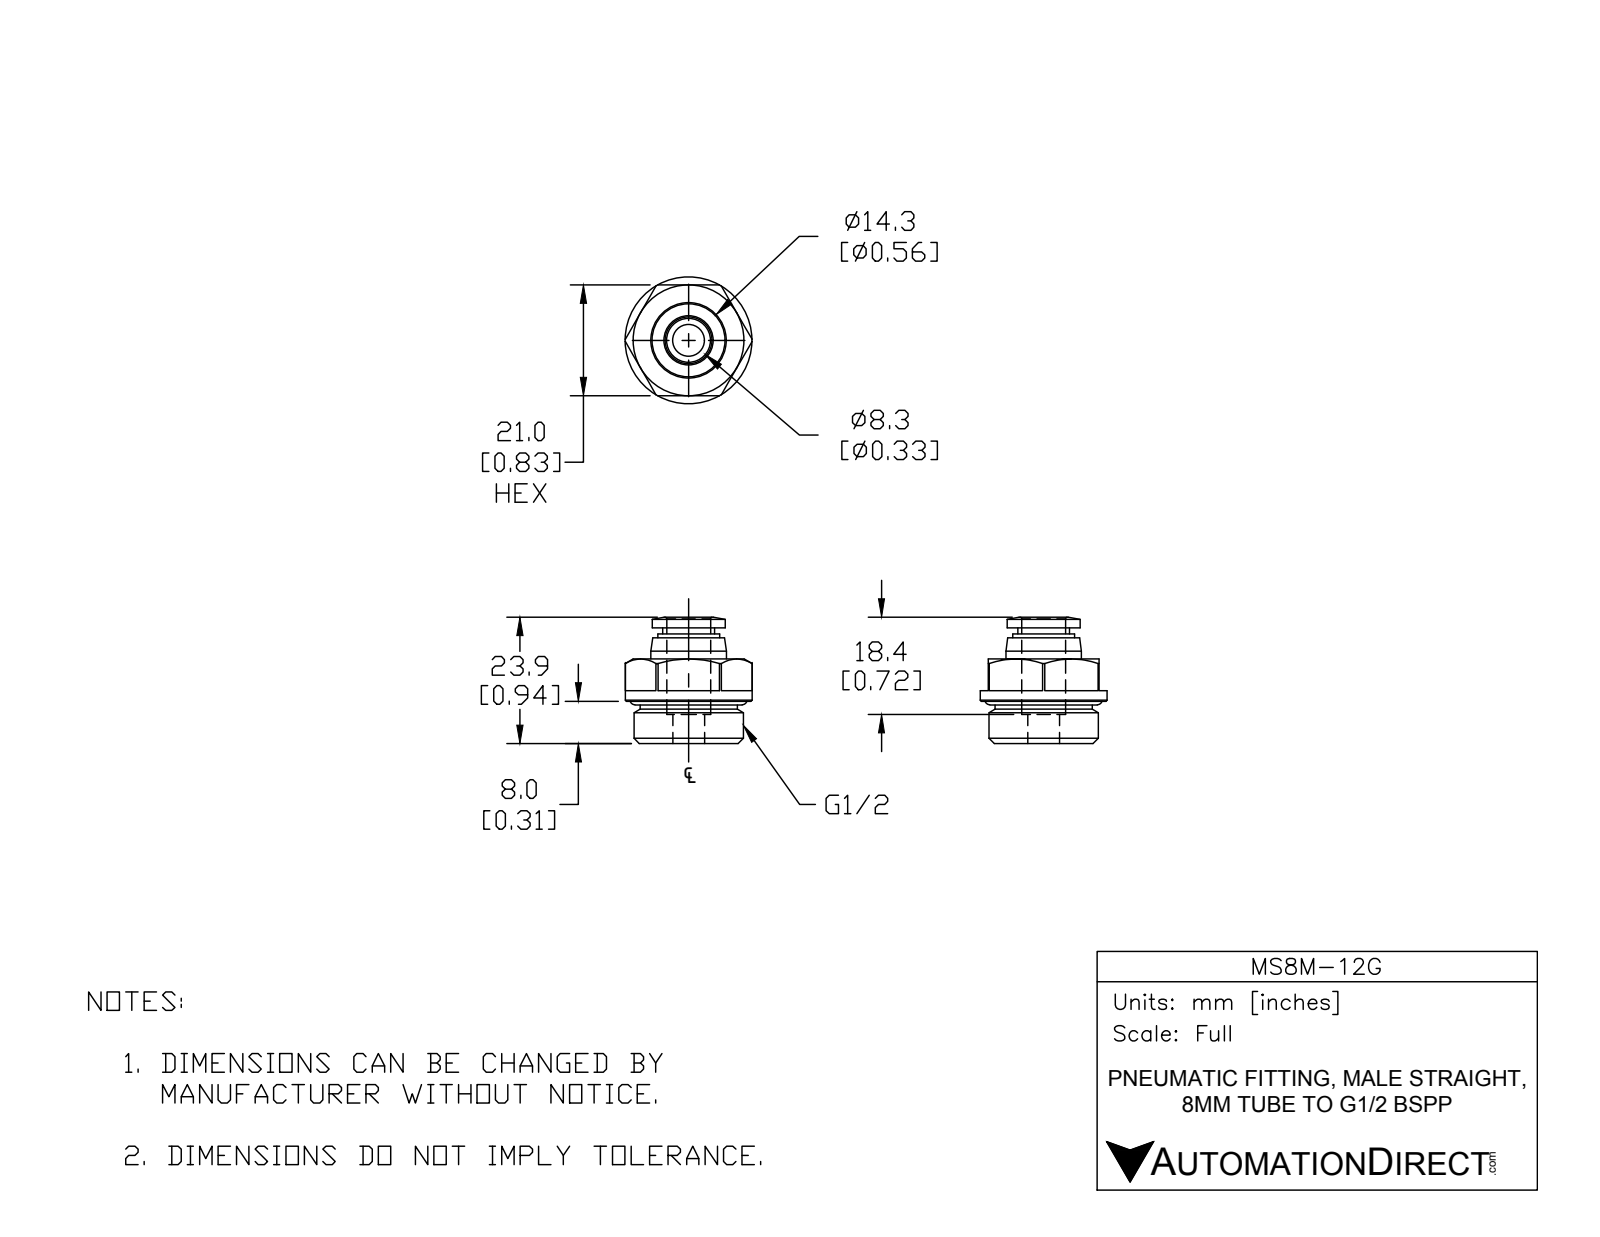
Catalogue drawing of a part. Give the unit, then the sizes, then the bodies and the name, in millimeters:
Units: millimetres
Overall size (bounding box): 24 × 24 × 23.9
Round holes (diameter × count): ⌀6 ×1, ⌀8.3 ×1
Round bosses / shafts (diameter × count): ⌀24 ×1, ⌀20.7 ×1, ⌀18.4 ×1, ⌀14.3 ×1, ⌀13.8 ×1, ⌀11.7 ×1, ⌀9.8 ×1
Main face-to-face distances: 21, 16, 10, 21.9, 5.9, 6, 11.9, 8, 20, 4
Volume: 5 700 mm³ · Surface area: 3 477 mm²
Bodies: 2 solids, 65 faces (21 planar, 18 cylindrical, 26 other)
Part name (STEP PRODUCT): MS8M-12G
STEP written by: SolidWorks 2018 (AUTOMOTIVE_DESIGN)
